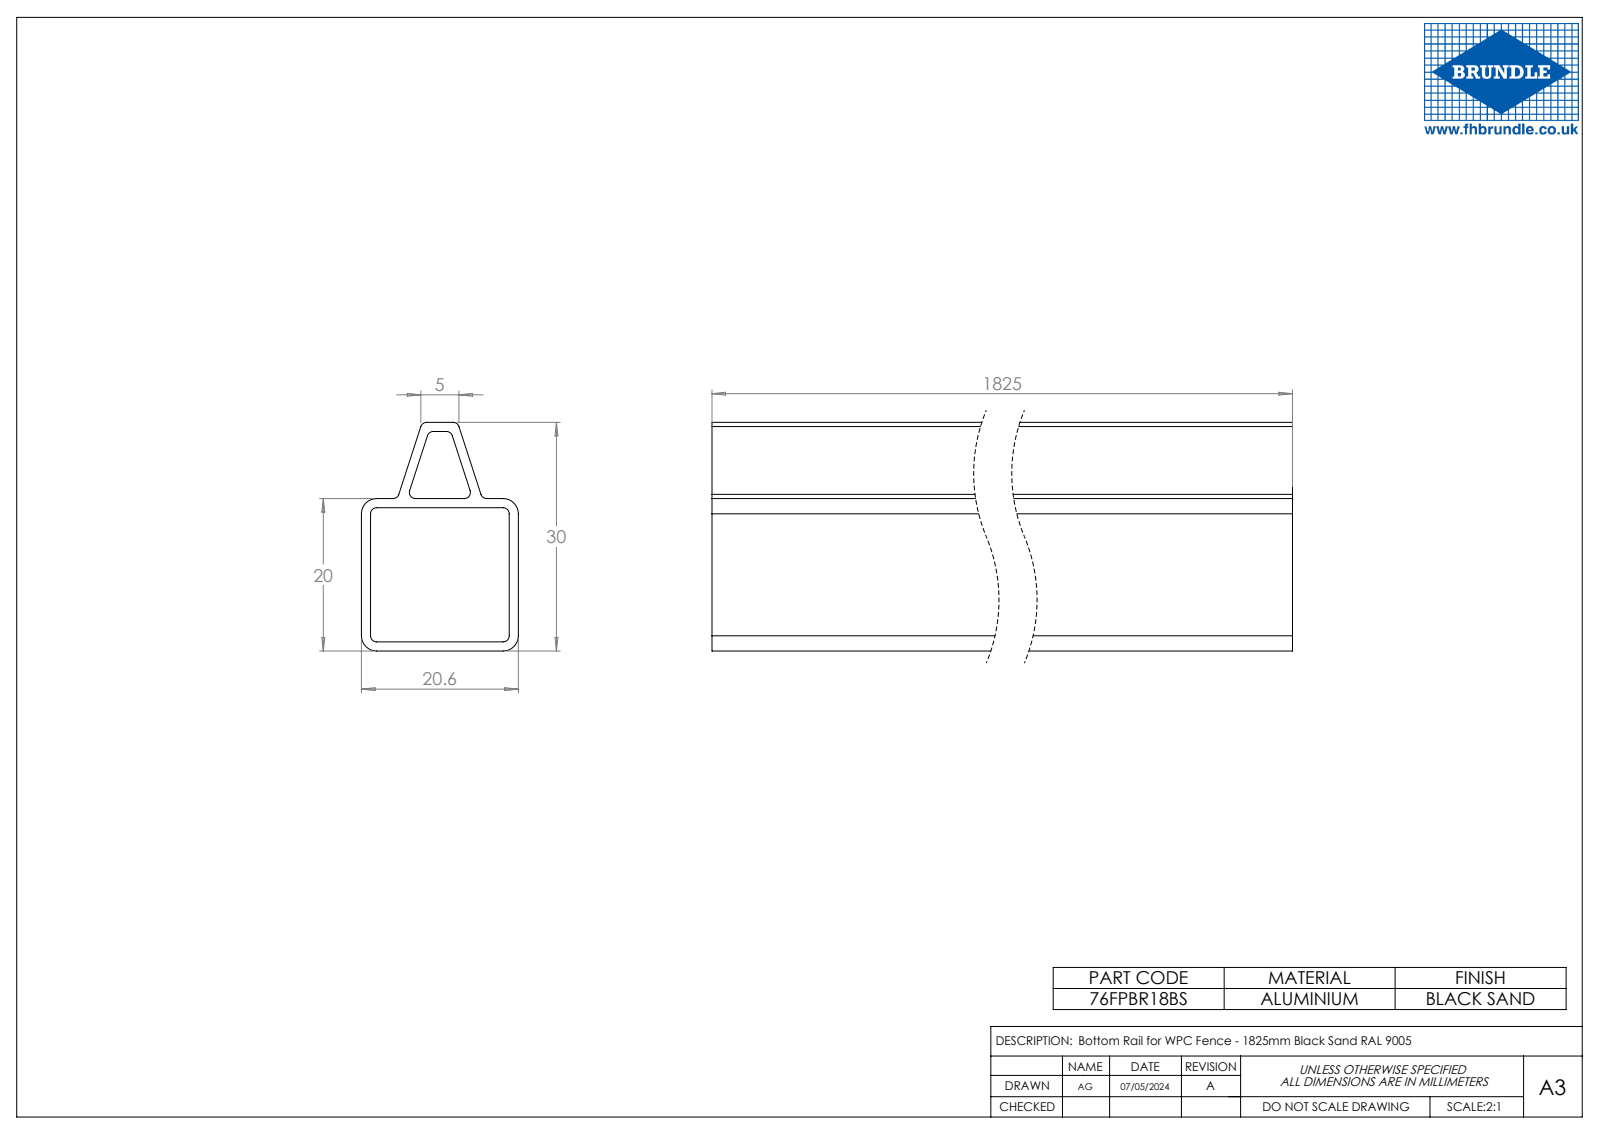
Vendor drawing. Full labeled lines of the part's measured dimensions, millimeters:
Part name (STEP PRODUCT): 72FPBR18BS
STEP written by: SolidWorks 2023 (CONFIG_CONTROL_DESIGN)
Units: millimetres
Bodies: 1 solid, 35 faces (18 planar, 17 cylindrical, 0 other)
Overall size (bounding box): 1825 × 30 × 20.6
Volume: 214 840 mm³ · Surface area: 347 370 mm²
Partial cylindrical surfaces — rounded edges, fillets, slot ends (radius × count): R0.8 ×12, R2 ×4
Main face-to-face distances: 1.2, 19.4, 18.8, 17.6, 20.6, 18.2, 20, 28.8, 10, 30
